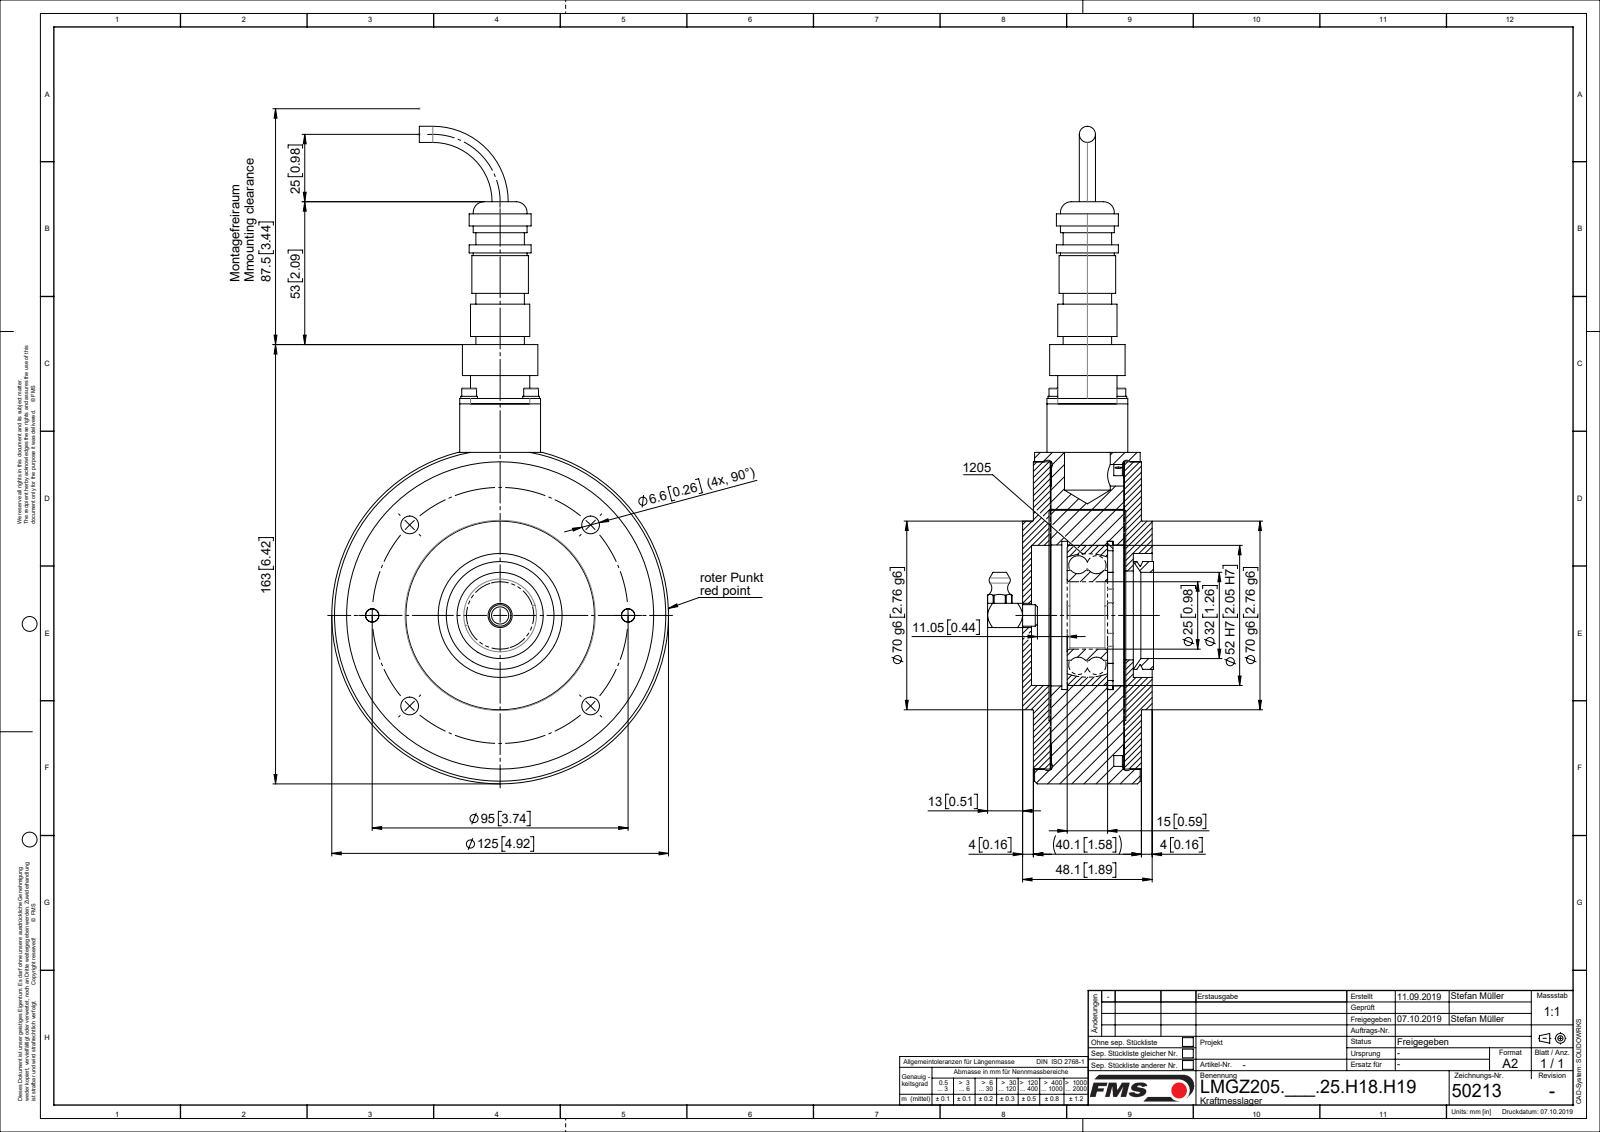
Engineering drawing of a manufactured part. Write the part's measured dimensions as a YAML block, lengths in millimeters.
part_name: "ZEICHNUNG7; L50213; L4832404; L47955 (+8 more)"
step_written_by: "Mechanical Desktop 2007 (CONFIG_CONTROL_DESIGN)"
units: millimeters
bodies: {solids: 21, faces: 421, planar: 107, cylindrical: 250, other: 64}
overall_size: [244, 125, 62.6]
volume: 490446
surface_area: 146653
round_holes:
  - {diameter: 6.6, count: 6}
  - {diameter: 2.6, count: 4}
  - {diameter: 3.2, count: 4}
  - {diameter: 3.4, count: 4}
  - {diameter: 5, count: 2}
  - {diameter: 11, count: 2}
  - {diameter: 8.68, count: 1}
  - {diameter: 25, count: 1}
  - {diameter: 31, count: 1}
  - {diameter: 33, count: 1}
  - {diameter: 37.9, count: 1}
  - {diameter: 46, count: 1}
round_bosses_or_shafts:
  - {diameter: 6.2, count: 4}
  - {diameter: 5.5, count: 4}
  - {diameter: 3, count: 4}
  - {diameter: 2.5, count: 4}
  - {diameter: 10, count: 3}
  - {diameter: 6, count: 3}
  - {diameter: 125, count: 1}
  - {diameter: 114, count: 1}
partial_cylinders:
  - {radius: 5, count: 8}
  - {radius: 4, count: 4}
  - {radius: 40.5, count: 1}
  - {radius: 47, count: 1}
face_to_face_distances: [27.25, 33.55, 6.3, 6.55, 33.8, 27, 27.5, 4, 10.55, 37.8]
hole_center_spacings: [47.5, 23, 36.36, 67.18, 87.77, 32.53, 95.01, 95]
